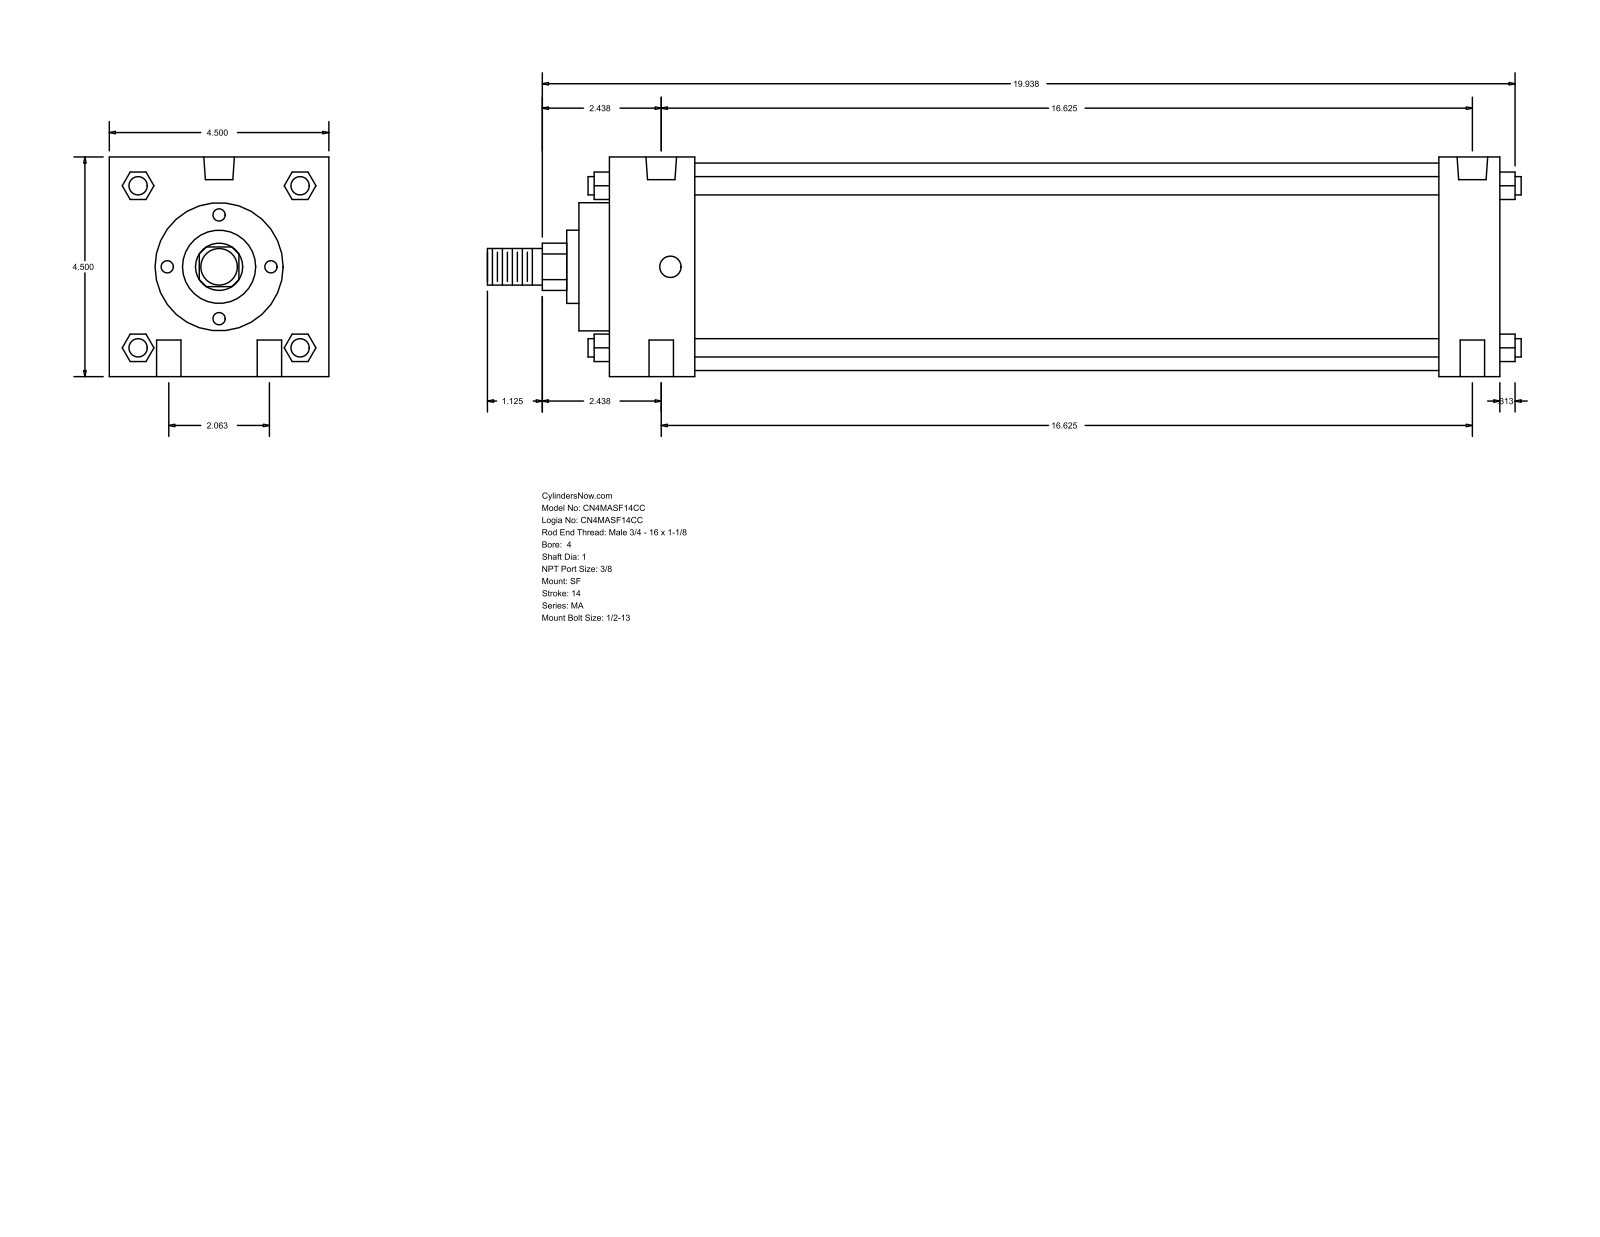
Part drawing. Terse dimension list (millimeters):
name: MA_SF__0400_1
written by: GSSL Pune (CONFIG_CONTROL_DESIGN)
unit: mm
bodies: 0 solids, 126 faces (95 planar, 31 cylindrical, 0 other)
size: 538.16 × 114.3 × 114.3
holes: 4× ⌀12.7, 2× ⌀11.11, 2× ⌀15.93
bosses: 4× ⌀9.53, 1× ⌀107.95, 1× ⌀66.67, 1× ⌀38.1, 1× ⌀25.4, 1× ⌀19.05
rounds: 1× R12.29
face distances: 114.3, 463.56, 431.81, 31.75, 44.46, 387.35, 419.1, 15.87, 60.33, 447.68
hole spacings: 26.19, 423.09, 422.28, 52.38, 425.52, 412.76
